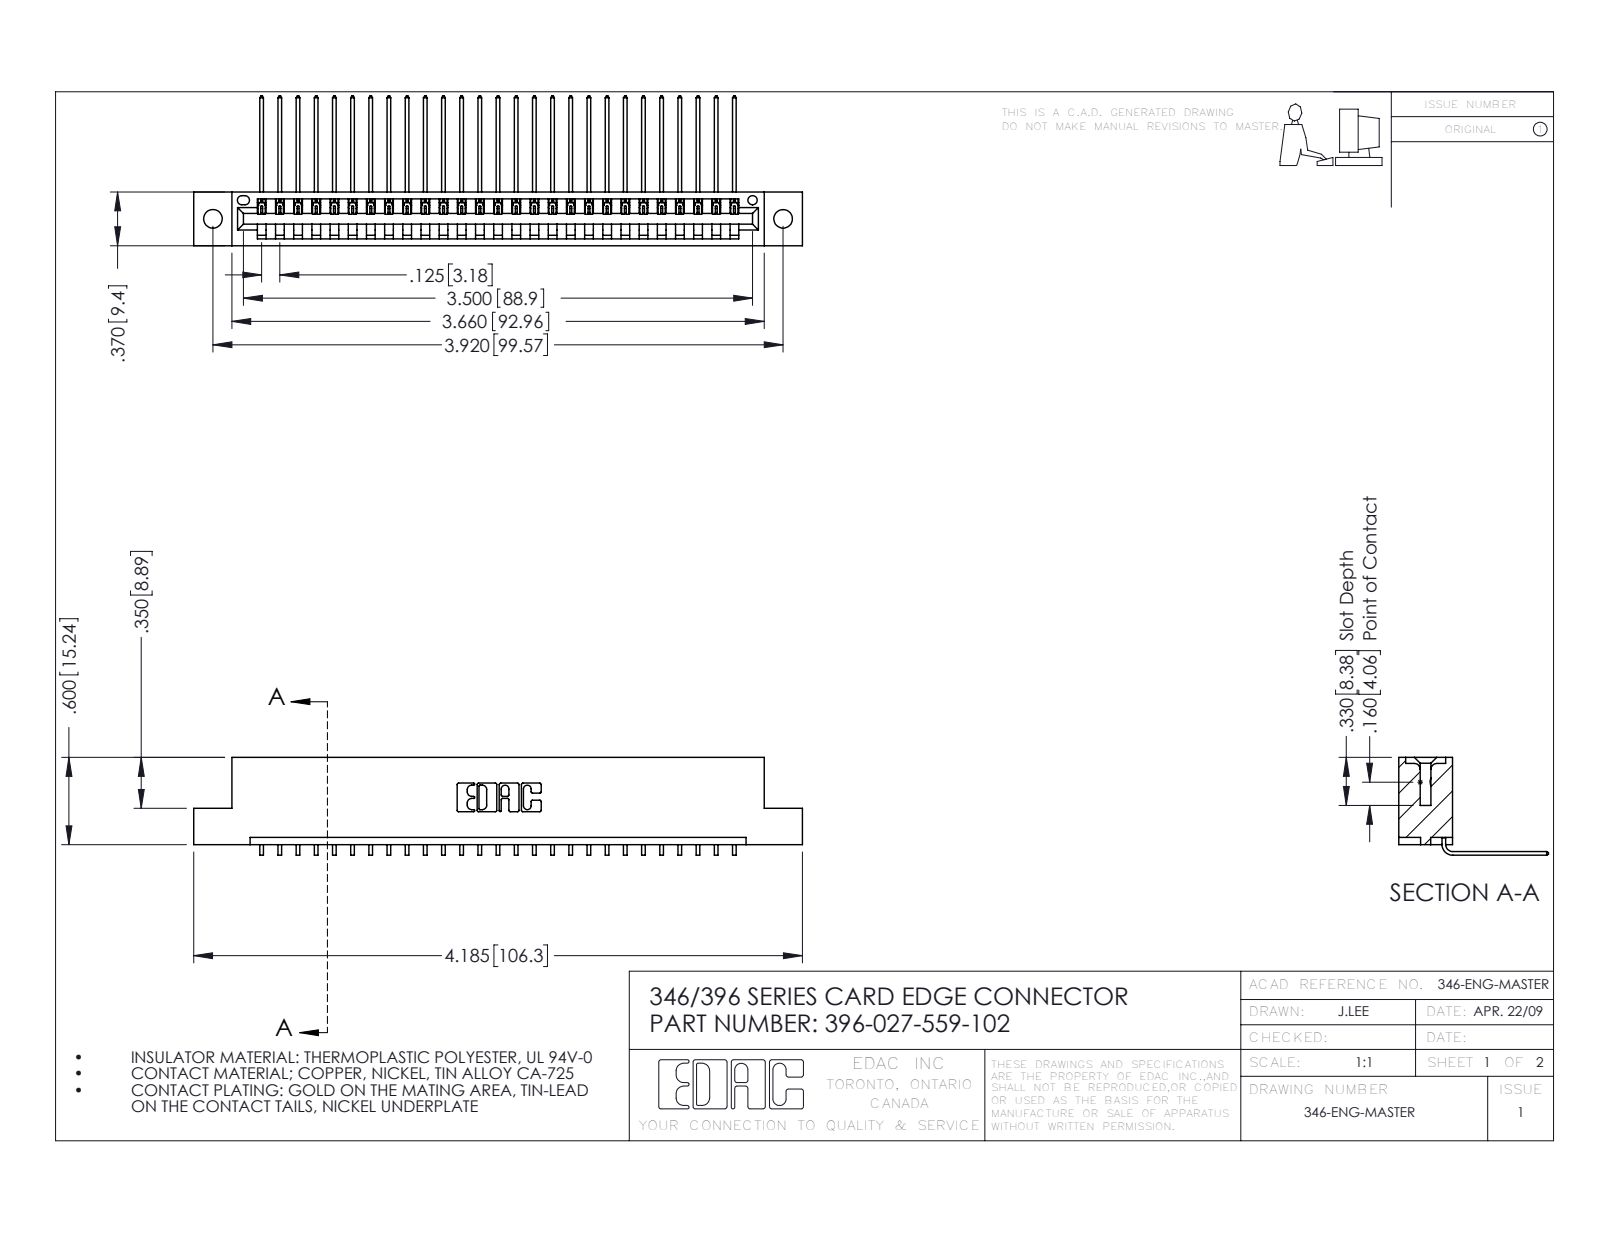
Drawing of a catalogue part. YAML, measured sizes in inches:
part_name: "396-027-559-102; 345-292-001_558 559 Tail - 1; 346 Part_Flush Mounting Lugs - 0.128 Dia"
step_written_by: "SolidWorks 2016 (CONFIG_CONTROL_DESIGN)"
units: inches
bodies: {solids: 28, faces: 1742, planar: 1210, cylindrical: 532, other: 0}
overall_size: [4.185, 1.03, 0.673]
volume: 0.618
surface_area: 19.78
round_holes:
  - {diameter: 0.128, count: 2}
  - {diameter: 0.064, count: 1}
partial_cylinders:
  - {radius: 0.006, count: 54}
  - {radius: 0.01, count: 22}
  - {radius: 0.007, count: 6}
  - {radius: 0.031, count: 6}
  - {radius: 0.026, count: 3}
  - {radius: 0.031, count: 2}
  - {radius: 0.04, count: 2}
  - {radius: 0.014, count: 1}
face_to_face_distances: [0.048, 0.322, 0.37, 0.25, 0.072, 0.025, 0.298, 0.148, 0.222, 0.1]
hole_center_spacings: [0.246, 3.712, 3.92]
